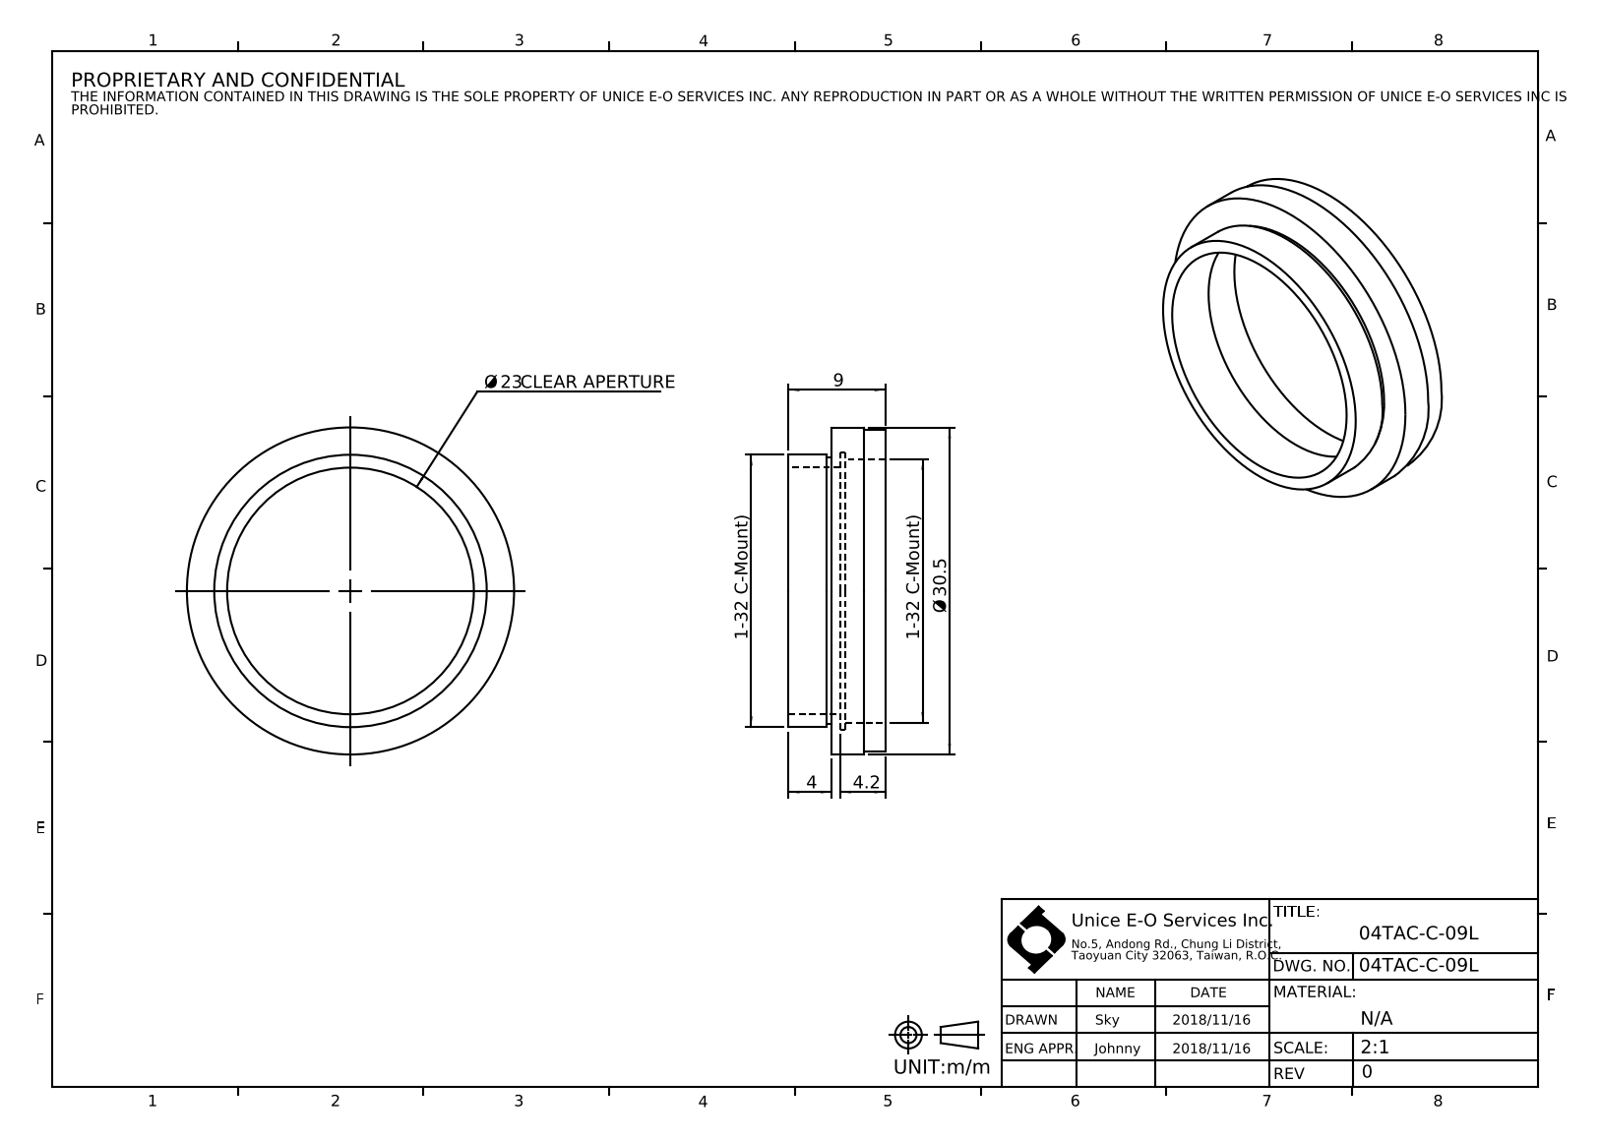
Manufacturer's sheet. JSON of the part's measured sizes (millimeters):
{"part_name": "04TAC-C-09L", "step_written_by": "SolidWorks 2016 (AUTOMOTIVE_DESIGN)", "units": "millimeters", "bodies": {"solids": 0, "faces": 19, "planar": 5, "cylindrical": 14, "other": 0}, "overall_size": [30.5, 30.5, 9], "round_holes": [[23, 1], [24.61, 1], [25.91, 1]], "round_bosses_or_shafts": [[30.5, 1], [30, 1], [25.4, 1], [24.89, 1]], "face_to_face_distances": [5, 4.2, 0.8, 9, 4.8, 4, 2, 2.2, 3, 7]}
